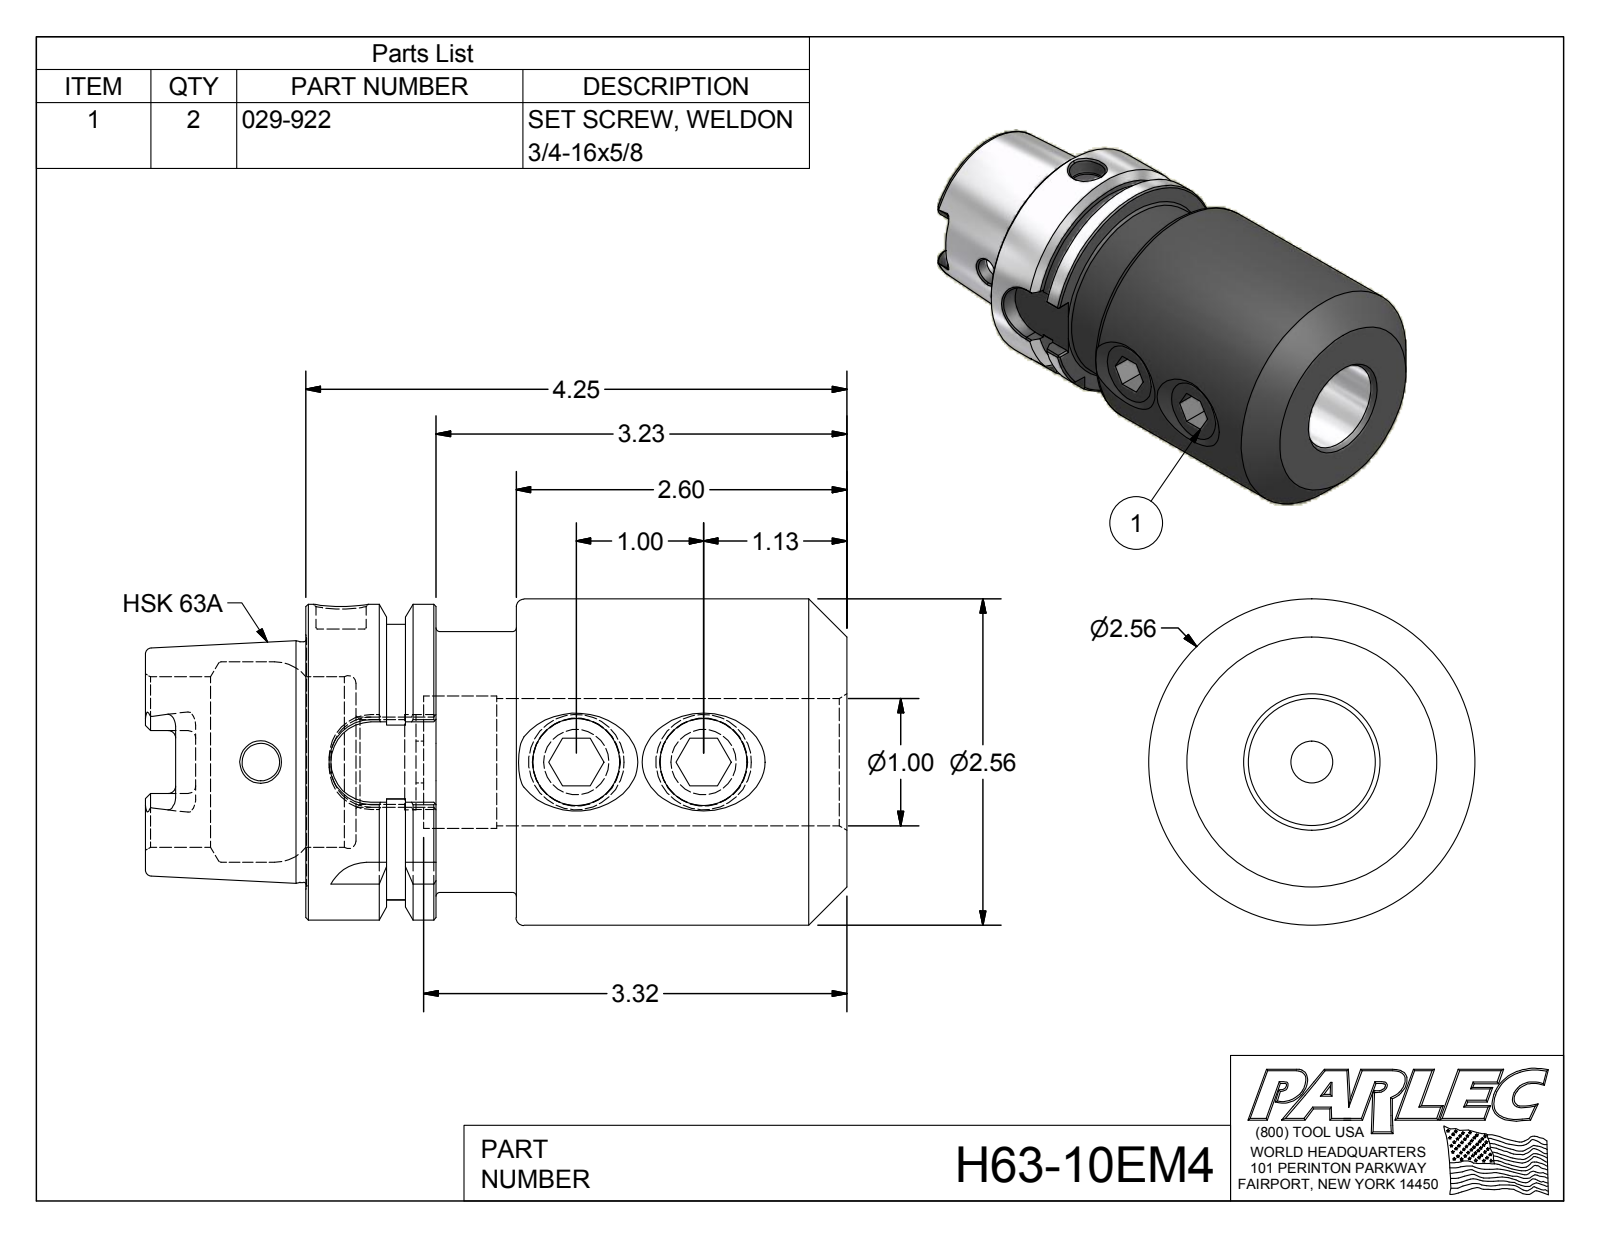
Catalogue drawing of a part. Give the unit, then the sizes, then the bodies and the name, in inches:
Units: inches
Overall size (bounding box): 5.51 × 2.563 × 2.563
Round holes (diameter × count): ⌀0.682 ×2, ⌀0.295 ×1, ⌀0.331 ×1, ⌀0.394 ×1, ⌀0.666 ×1, ⌀0.749 ×1, ⌀1 ×1, ⌀1.04 ×1, ⌀1.339 ×1, ⌀1.575 ×1
Round bosses / shafts (diameter × count): ⌀0.75 ×2, ⌀2.563 ×1, ⌀2.48 ×1, ⌀2.047 ×1, ⌀1.891 ×1
Partial cylindrical surfaces — rounded edges, fillets, slot ends (radius × count): R0.059 ×6, R0.113 ×4, R0.315 ×4, R1.083 ×1
Main face-to-face distances: 0.63, 1.654, 4.25, 1.26, 2.596, 1.024, 0.241, 0.389, 3.226, 0.394
Hole centre spacings: 1, 2.48, 3.48
Volume: 17.27 in³ · Surface area: 79.13 in²
Bodies: 3 solids, 173 faces (77 planar, 41 cylindrical, 55 other)
Part name (STEP PRODUCT): H63-10EM4; H63-10EM4-1; 029-922
STEP written by: Autodesk Inventor 2012 (AUTOMOTIVE_DESIGN)
